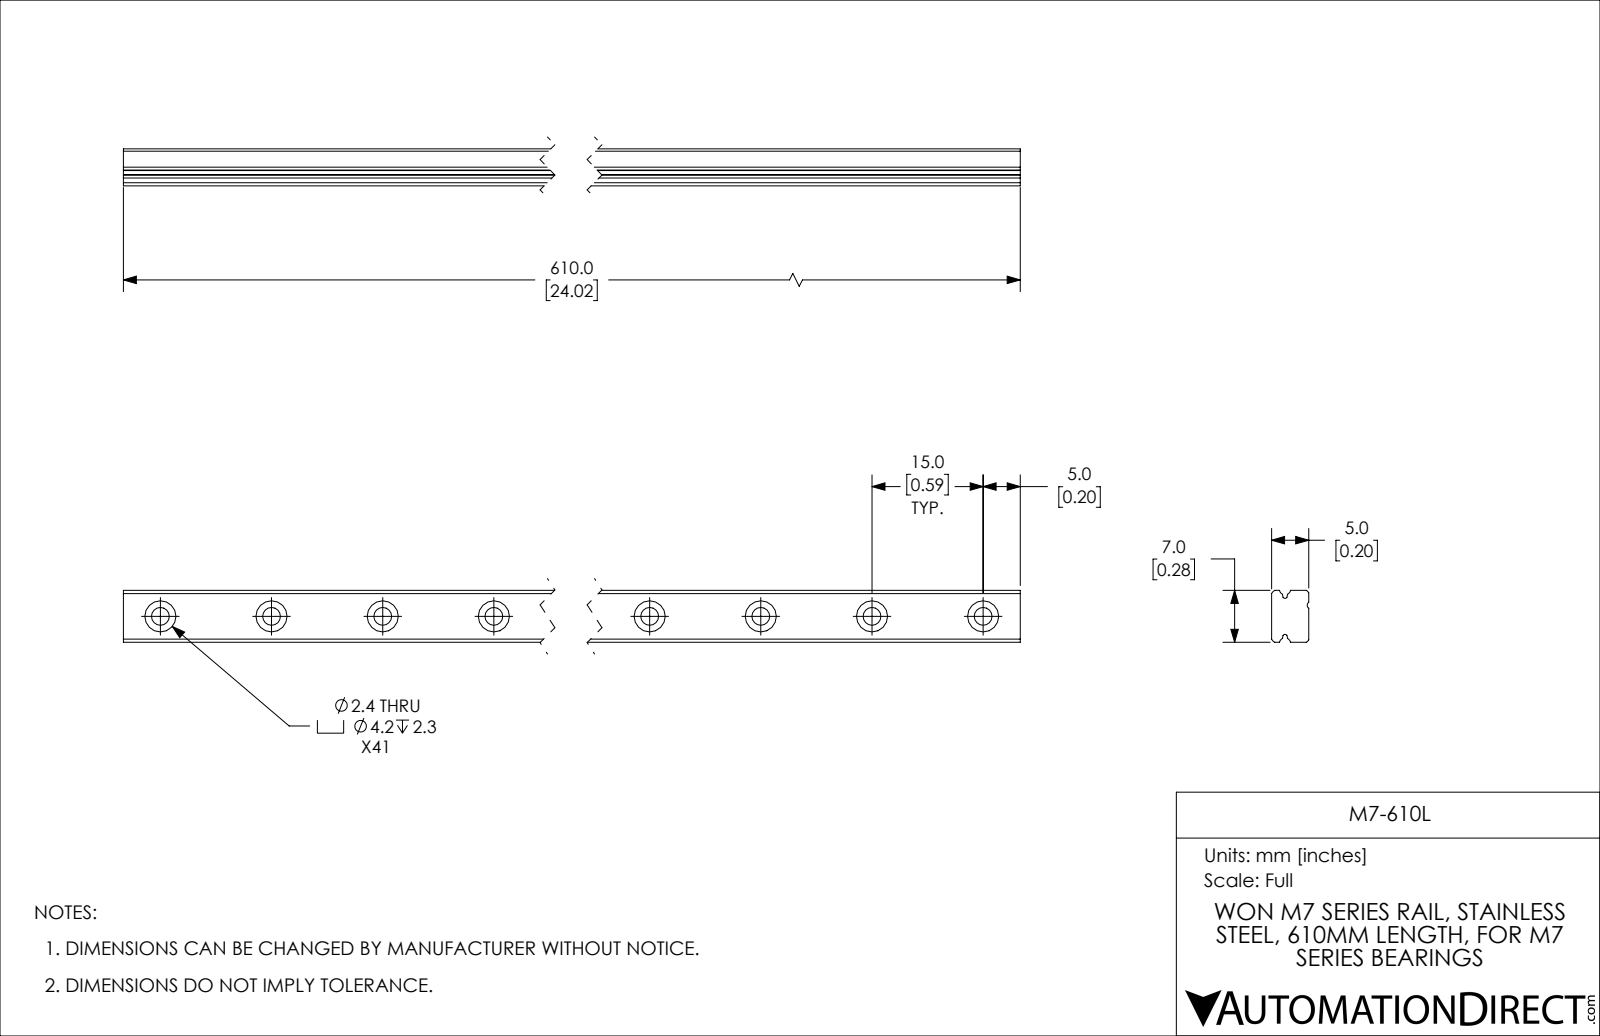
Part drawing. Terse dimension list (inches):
name: M7-610L
written by: SolidWorks 2019 (CONFIG_CONTROL_DESIGN)
unit: in
bodies: 1 solid, 230 faces (54 planar, 176 cylindrical, 0 other)
size: 24.016 × 0.276 × 0.197
volume: 1.111 in³; area: 27.28 in²
holes: 41× ⌀0.094, 41× ⌀0.165
rounds: 2× R0.013, 2× R0.03, 2× R0.037, 2× R0.039, 1× R0.02
face distances: 0.197, 0.276, 0.014, 0.106, 0.091, 24.016
hole spacings: 1.181, 2.362, 3.543, 4.724, 5.906, 0.591, 7.087, 1.772
